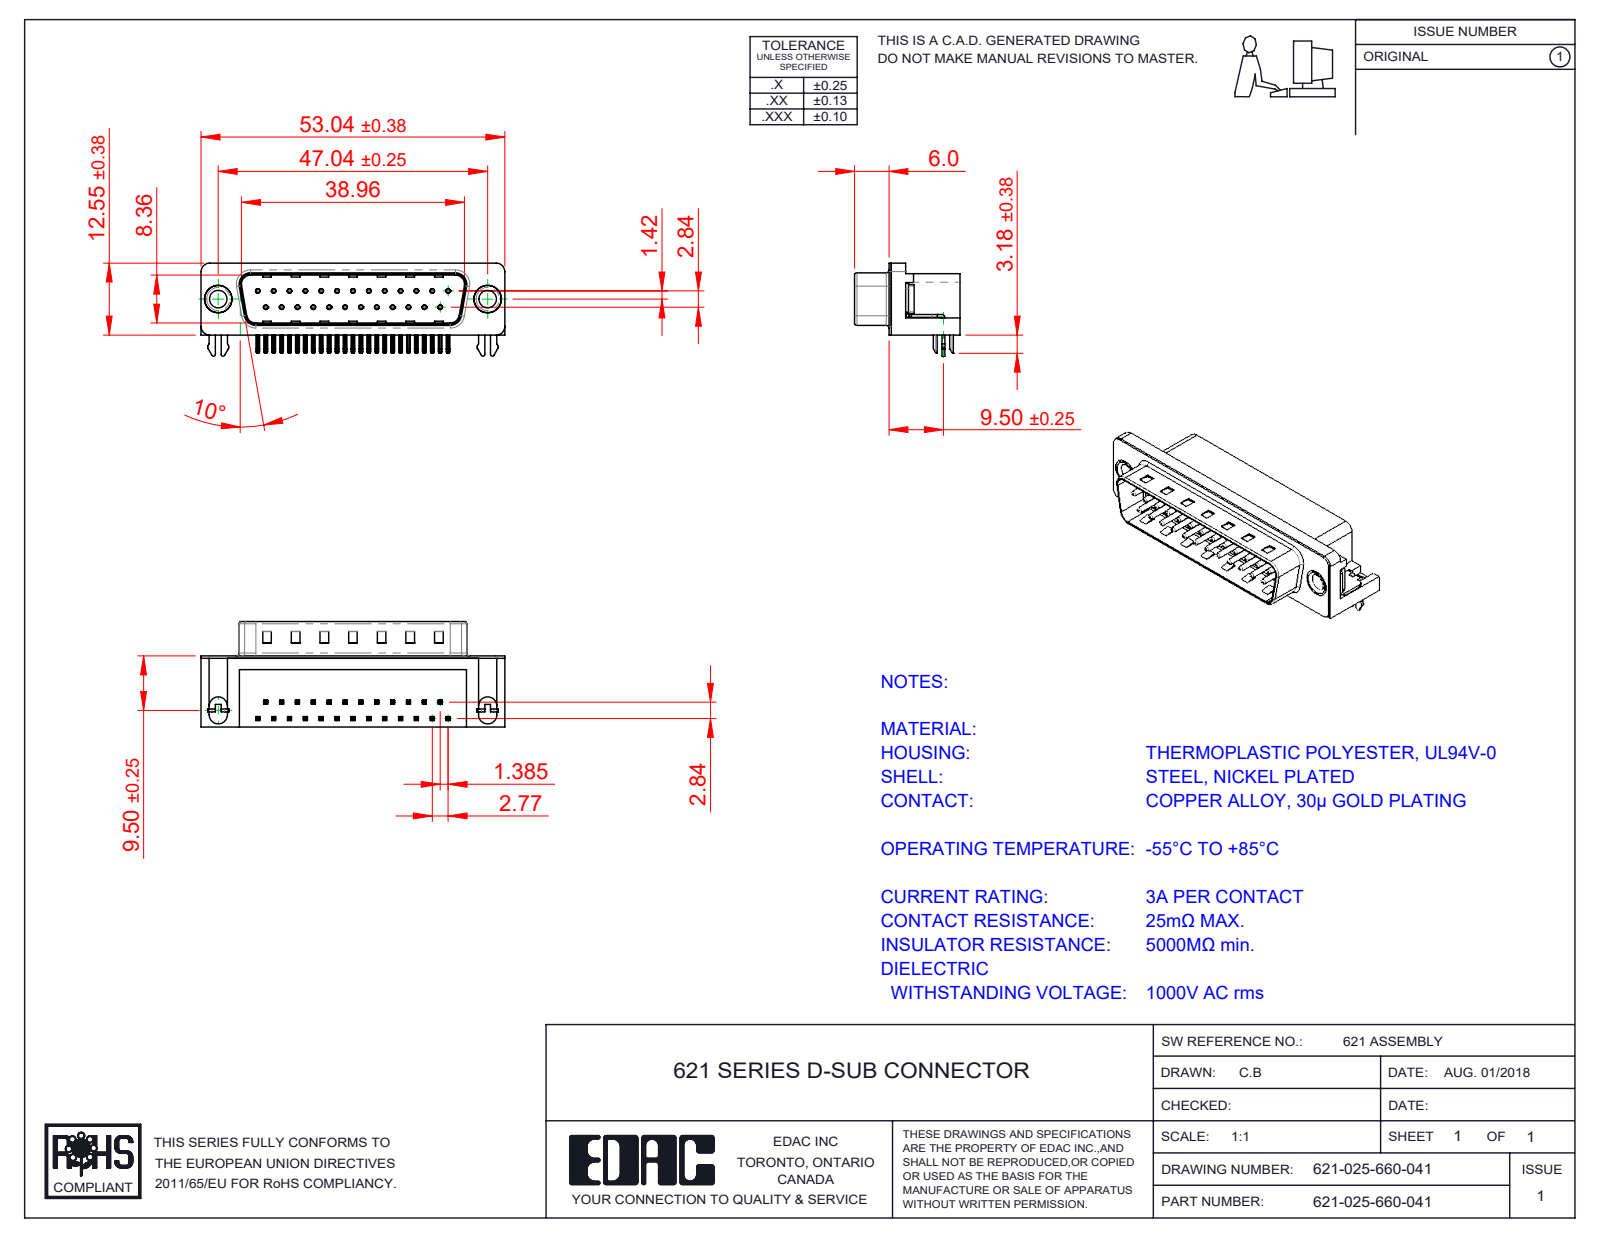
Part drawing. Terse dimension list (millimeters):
name: 621 Housing_25 Socket; 621 4 Prong Board Lock; 621 Contact Top; 621 Shell_25 Socket (+3 more)
written by: SolidWorks 2016 (CONFIG_CONTROL_DESIGN)
unit: mm
bodies: 31 solids, 2343 faces (1447 planar, 647 cylindrical, 249 other)
size: 53.04 × 18.4 × 16.25
volume: 6 345 mm³; area: 7 734 mm²
holes: 25× ⌀0.35, 25× ⌀0.8, 2× ⌀2, 2× ⌀3.05, 2× ⌀4, 2× ⌀4.8, 2× ⌀5
bosses: 25× ⌀0.75, 2× ⌀4.9, 2× ⌀4.75, 2× ⌀3.85, 2× ⌀3
rounds: 112× R0.25, 50× R0.12, 16× R1, 9× R0.5, 8× R1.6, 7× R1.5, 4× R0.9, 4× R2
face distances: 0.4, 12, 10.35, 2.1, 8.76, 10.46, 1.7, 10.86, 12.4, 9
hole spacings: 3.16, 2.77, 5.54, 8.31, 11.08, 13.85, 16.62, 5.03
